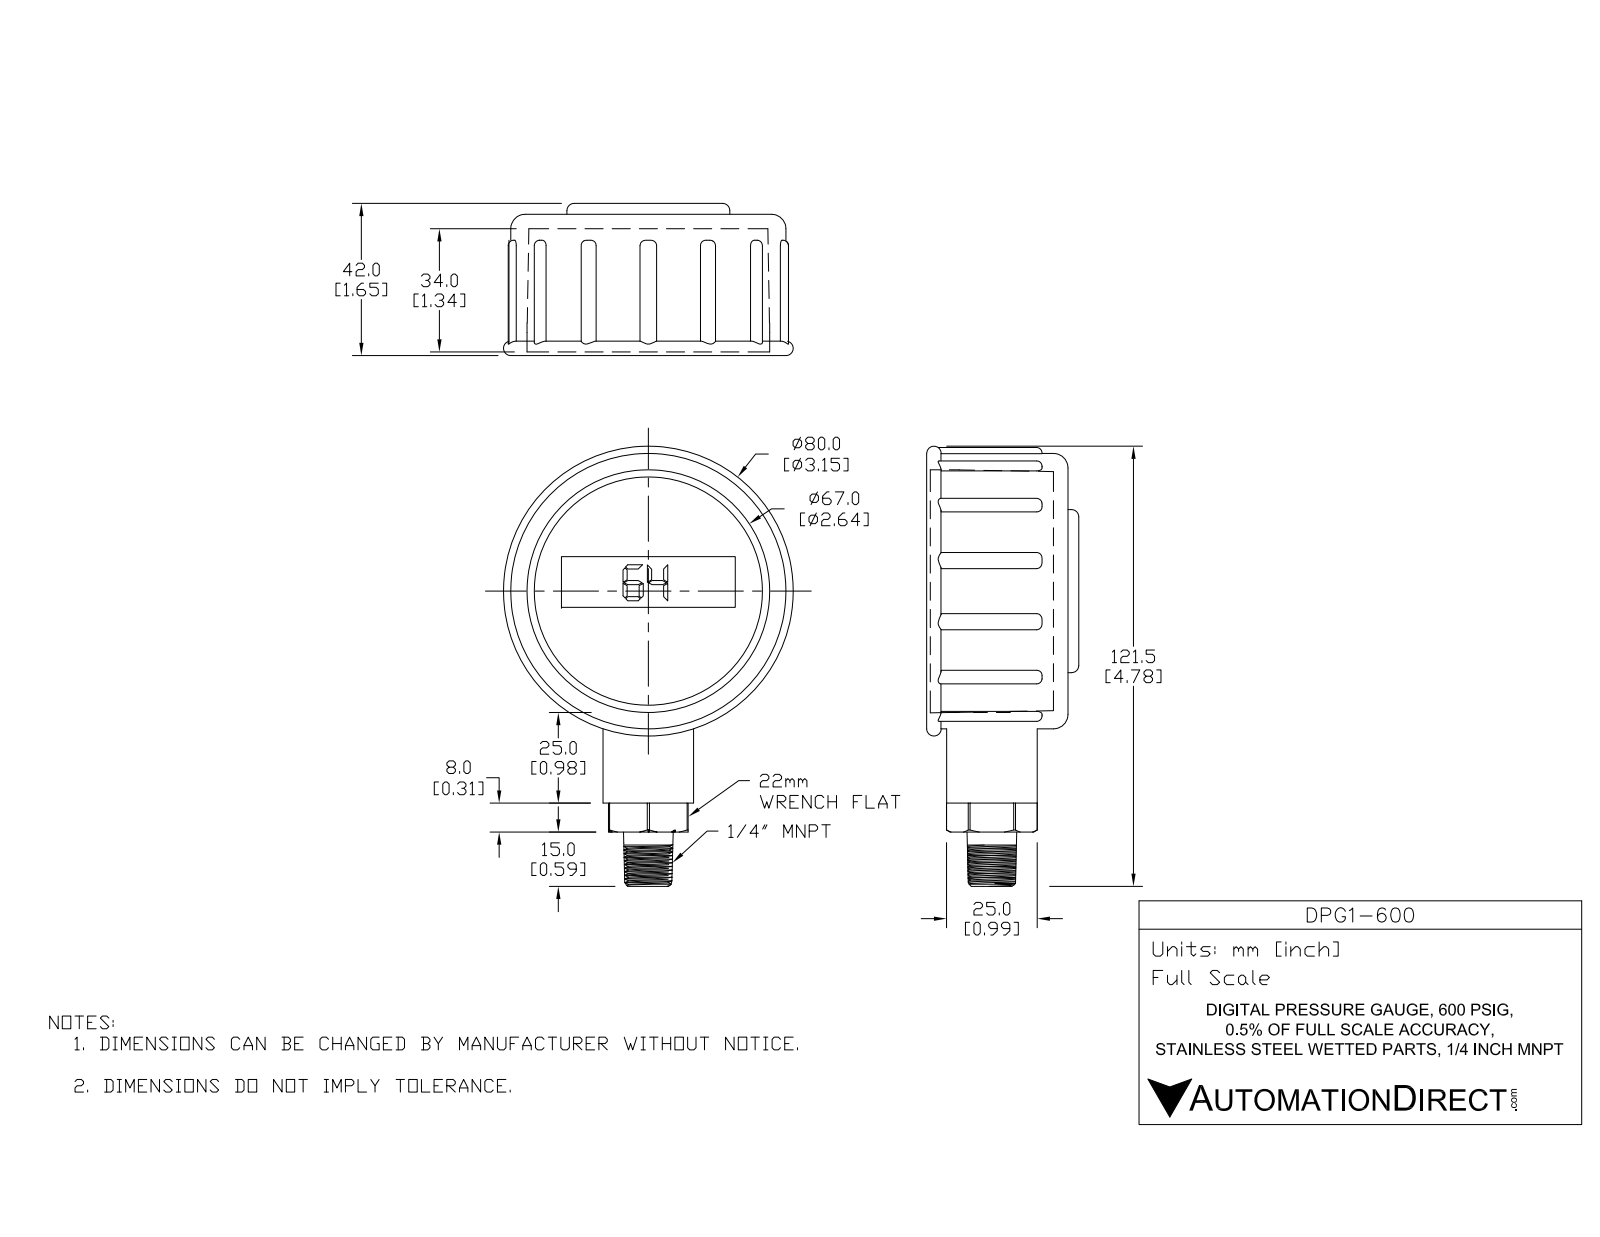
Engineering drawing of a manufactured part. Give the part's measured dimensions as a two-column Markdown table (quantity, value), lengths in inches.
| quantity | value |
| --- | --- |
| part name | DPG1-600 |
| STEP written by | SolidWorks 2021 (CONFIG_CONTROL_DESIGN) |
| units | inches |
| bodies | 4 solids, 181 faces (71 planar, 49 cylindrical, 61 other) |
| overall size | 4.788 × 3.15 × 1.654 |
| volume | 11.97 in³ |
| surface area | 71.27 in² |
| round holes (diameter × count) | 2.48 × 1, 2.645 × 1 |
| round bosses / shafts (diameter × count) | 2.992 × 1, 2.638 × 1, 1.772 × 1, 0.984 × 1, 0.394 × 1 |
| partial cylindrical surfaces (radius × count) | 0.094 × 13, 0.335 × 6, 1.496 × 1 |
| main face-to-face distances | 1.337, 0.157, 1.494, 0.118, 0.276, 1.612, 1.654, 1.535, 1.378, 0.041 |
